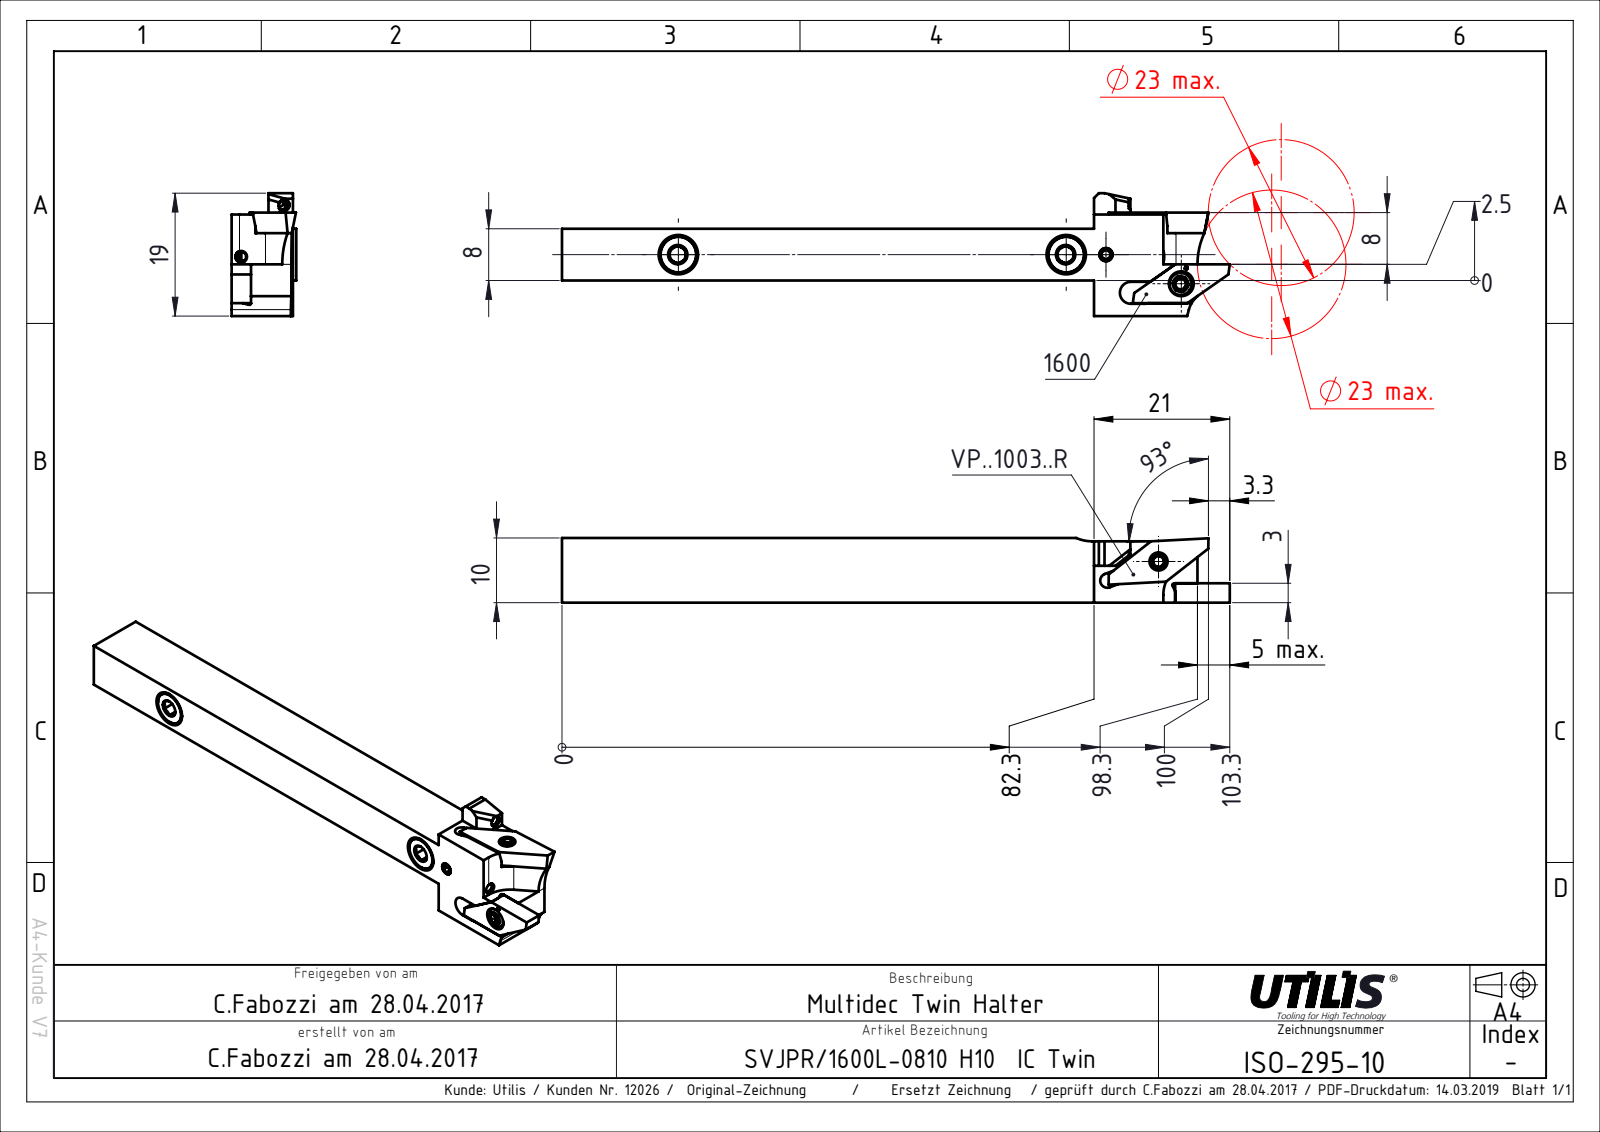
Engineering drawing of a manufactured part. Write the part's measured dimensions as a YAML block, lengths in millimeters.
part_name: "ISO-295-10"
step_written_by: "SolidWorks 2016 (AUTOMOTIVE_DESIGN)"
units: millimeters
bodies: {solids: 1, faces: 81, planar: 67, cylindrical: 12, other: 2}
overall_size: [103.3, 19, 10]
volume: 8810
surface_area: 4330
partial_cylinders:
  - {radius: 0.25, count: 2}
  - {radius: 6.1, count: 2}
  - {radius: 0.5, count: 1}
  - {radius: 1.1, count: 1}
  - {radius: 1.55, count: 1}
  - {radius: 1.7, count: 1}
  - {radius: 4.1, count: 1}
  - {radius: 5.1, count: 1}
face_to_face_distances: [8, 10, 5.5, 13.5, 2.5, 16, 82.3, 10.5, 2.2, 9.53]
